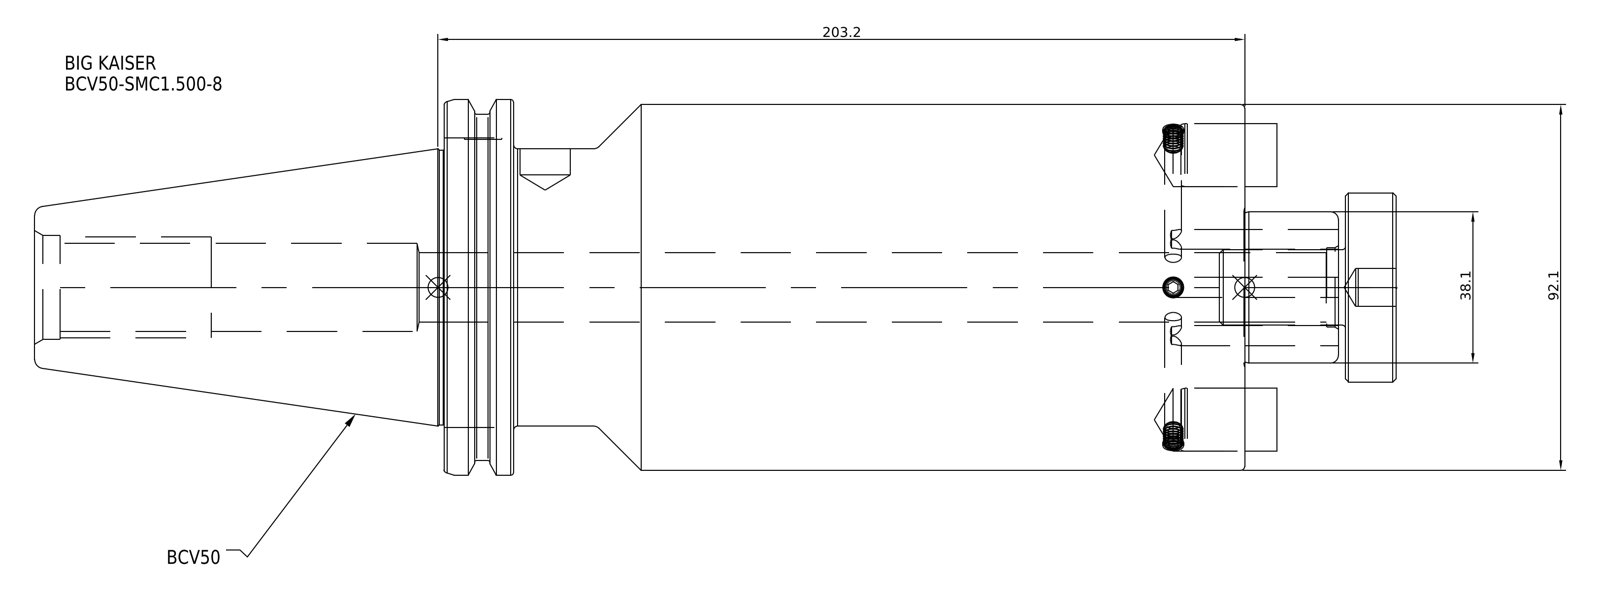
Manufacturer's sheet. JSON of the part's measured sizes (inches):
{"part_name": "BCV50-SMC1_500-8", "step_written_by": "SolidWorks 2021 (CONFIG_CONTROL_DESIGN)", "units": "inches", "bodies": {"solids": 1, "faces": 39, "planar": 17, "cylindrical": 14, "other": 8}, "overall_size": [12.318, 3.875, 3.875], "volume_in3": 91.29, "surface_area_in2": 159.9, "round_holes": [[0.687, 1]], "round_bosses_or_shafts": [[3.875, 1], [3.626, 1], [3.594, 1], [2.75, 1]], "face_to_face_distances": [7.941, 7.25, 0.691, 12, 4.75, 4.059, 0.625, 0.318, 7.568, 8.259]}
